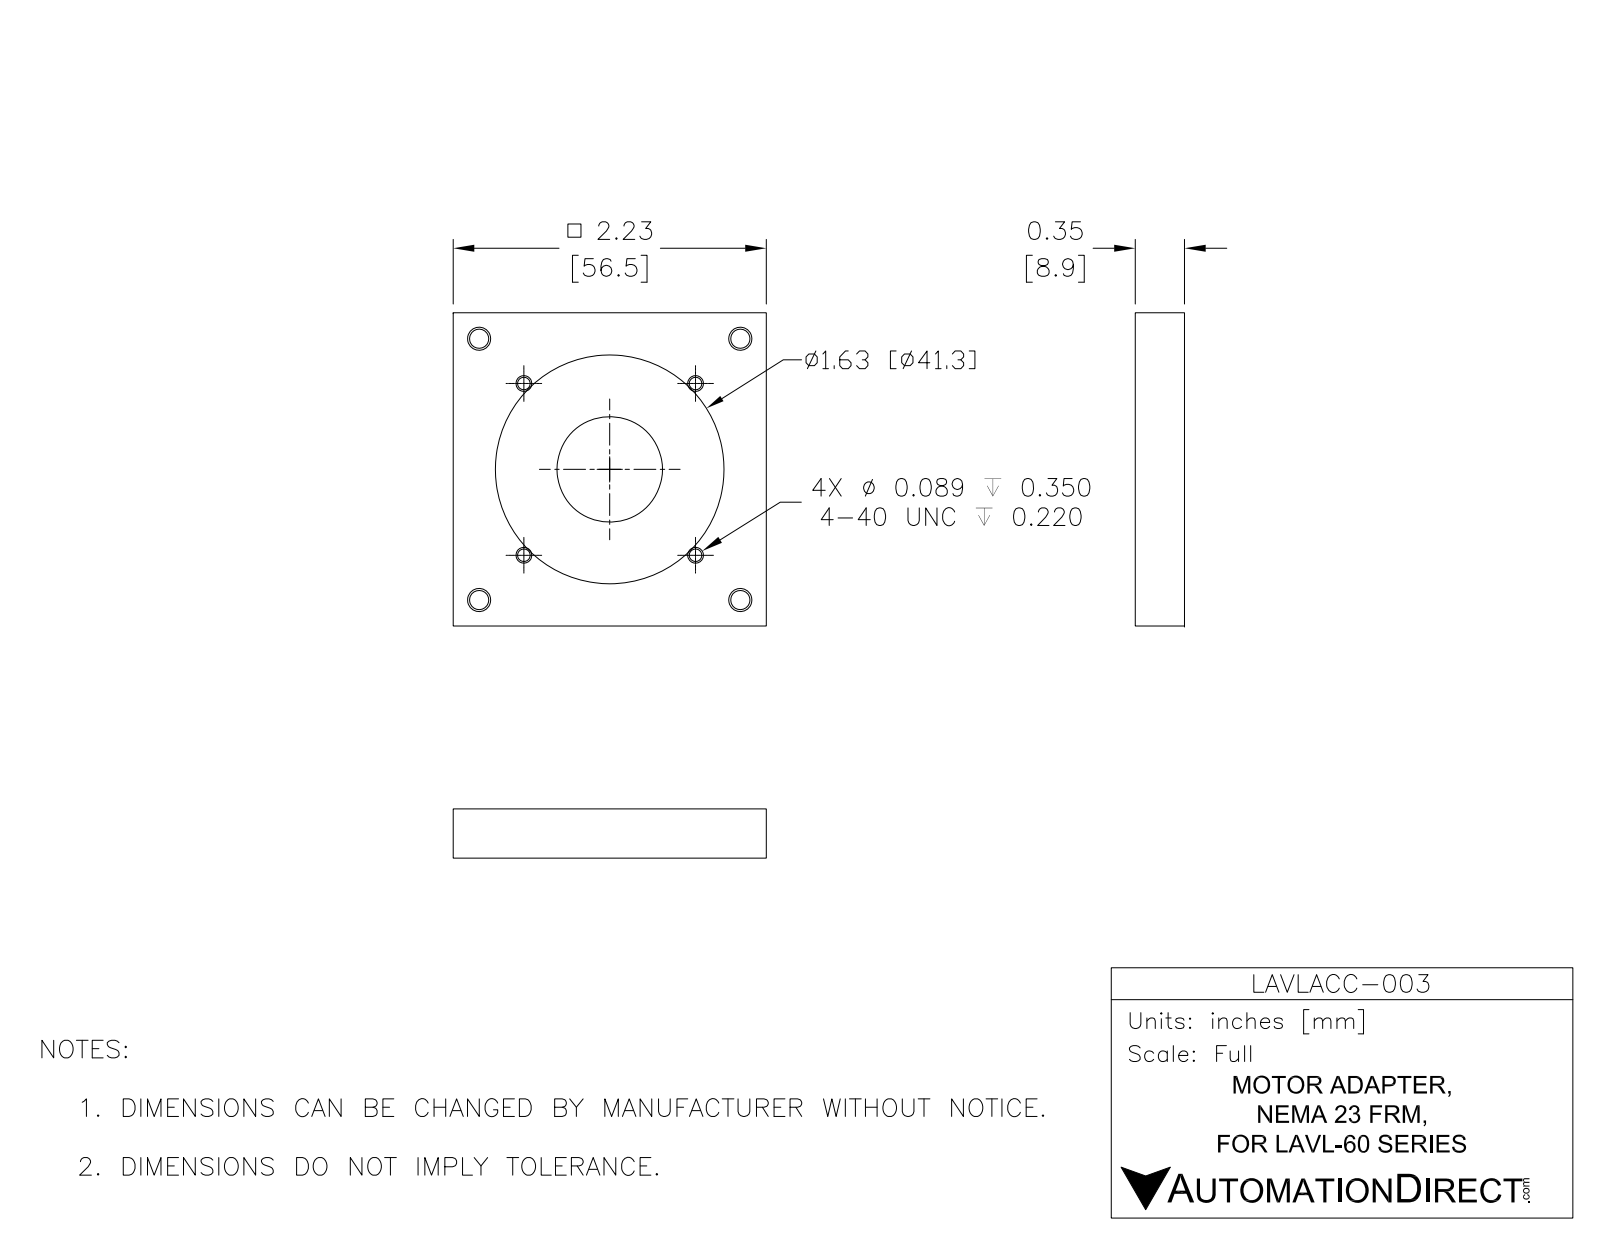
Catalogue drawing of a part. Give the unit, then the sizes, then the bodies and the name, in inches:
Units: inches
Overall size (bounding box): 2.225 × 2.225 × 0.35
Round holes (diameter × count): ⌀0.089 ×4, ⌀0.136 ×4, ⌀0.75 ×1, ⌀1.625 ×1
Main face-to-face distances: 0.35, 0.225, 0.125, 2.225
Hole centre spacings: 1.57, 0.45, 0.863, 1.22, 1.312, 1.856, 2.175, 1.725
Volume: 1.345 in³ · Surface area: 14.13 in²
Bodies: 1 solid, 27 faces (7 planar, 20 cylindrical, 0 other)
Part name (STEP PRODUCT): LAVLACC-003
STEP written by: SolidWorks 2015 (AUTOMOTIVE_DESIGN)
